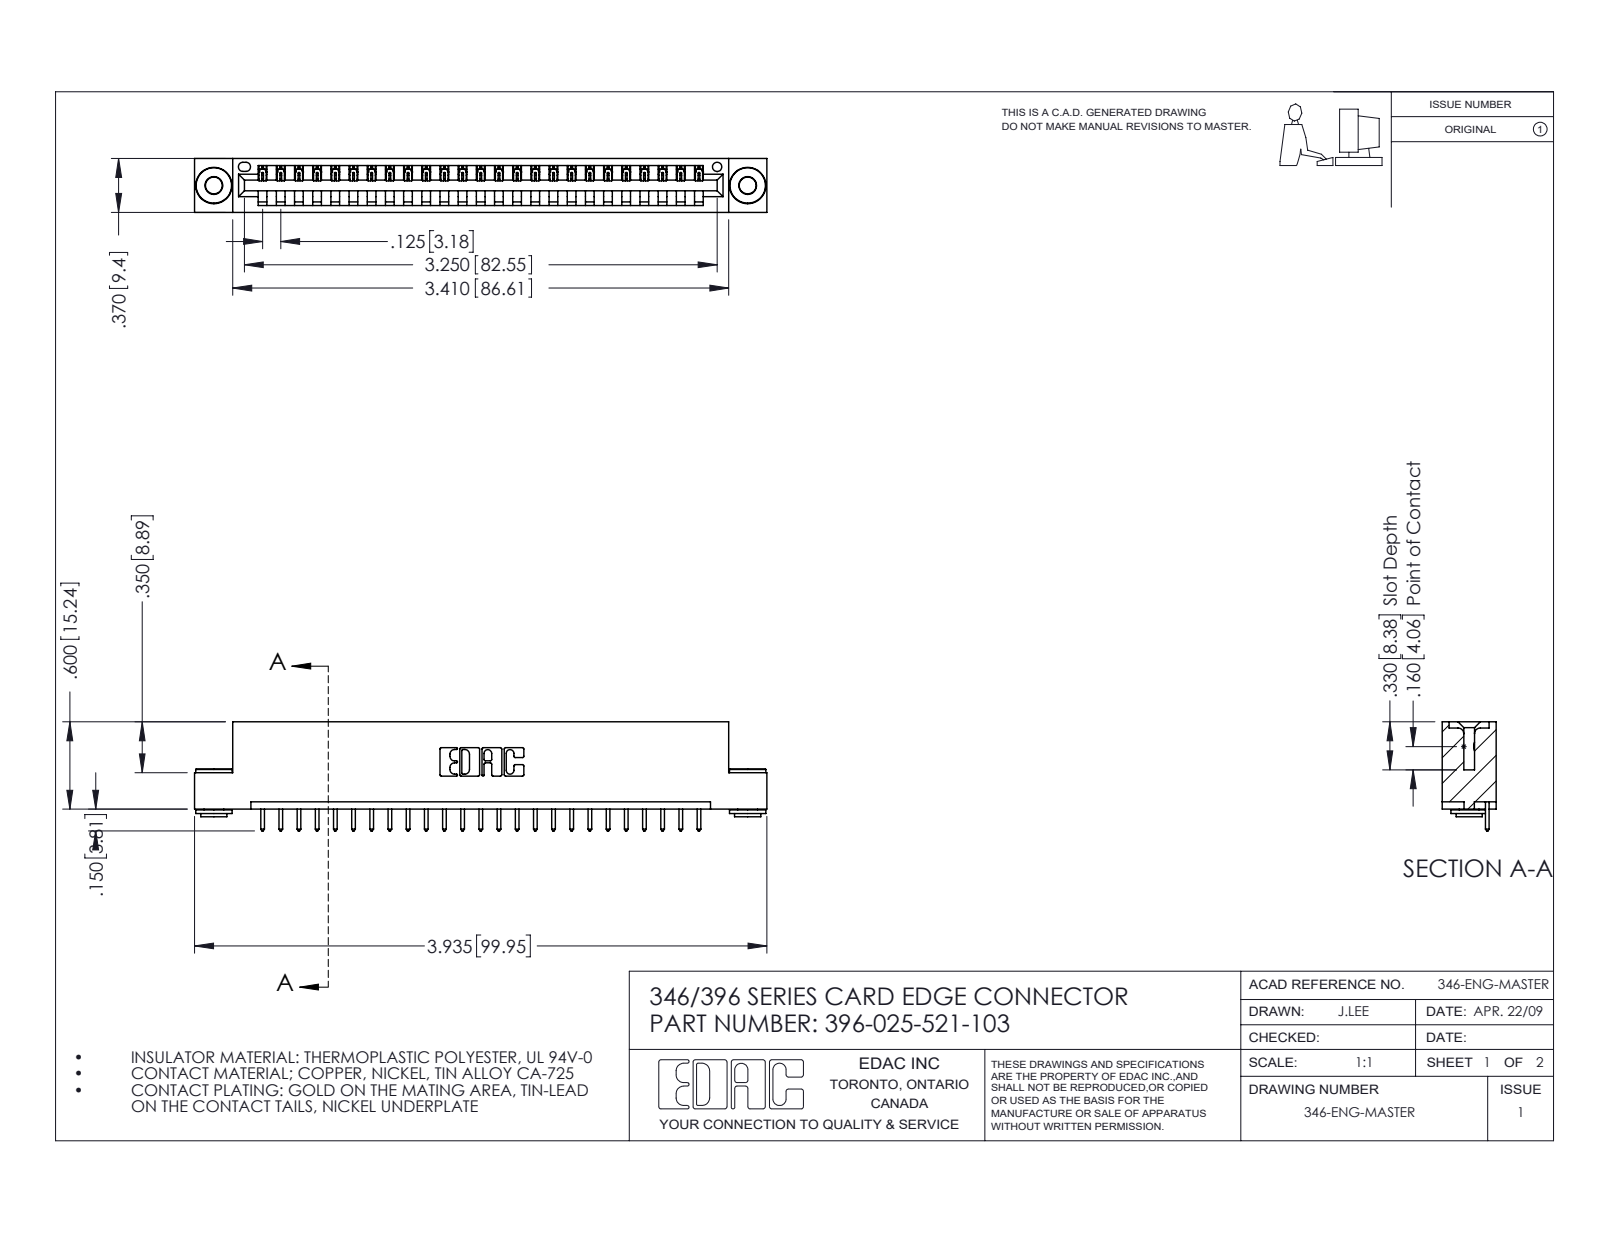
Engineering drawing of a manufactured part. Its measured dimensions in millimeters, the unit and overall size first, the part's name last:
Units: millimetres
Overall size (bounding box): 99.9 × 19.1 × 9.4
Round holes (diameter × count): ⌀2.9 ×2, ⌀4 ×2, ⌀1.6 ×1
Round bosses / shafts (diameter × count): ⌀6.4 ×2, ⌀4.6 ×2, ⌀3.5 ×2
Partial cylindrical surfaces — rounded edges, fillets, slot ends (radius × count): R0.2 ×50, R0.3 ×50, R0.3 ×22, R0.2 ×6, R0.8 ×6, R0.7 ×3, R0.8 ×2, R1 ×2
Main face-to-face distances: 1.2, 8.2, 9.4, 6.4, 0.6, 1.8, 7.6, 3.8, 5.6, 2.5
Hole centre spacings: 6.2, 87.9, 93.2
Volume: 9 410 mm³ · Surface area: 11 500 mm²
Bodies: 28 solids, 1610 faces (1086 planar, 516 cylindrical, 8 other)
Part name (STEP PRODUCT): 345-292-001_345-293-121; 345-250-002_345-250-002-102; 346 Part_Flush Mounting Lugs - 0.156 Dia-TH; 396-025-521-103
STEP written by: SolidWorks 2016 (CONFIG_CONTROL_DESIGN)
